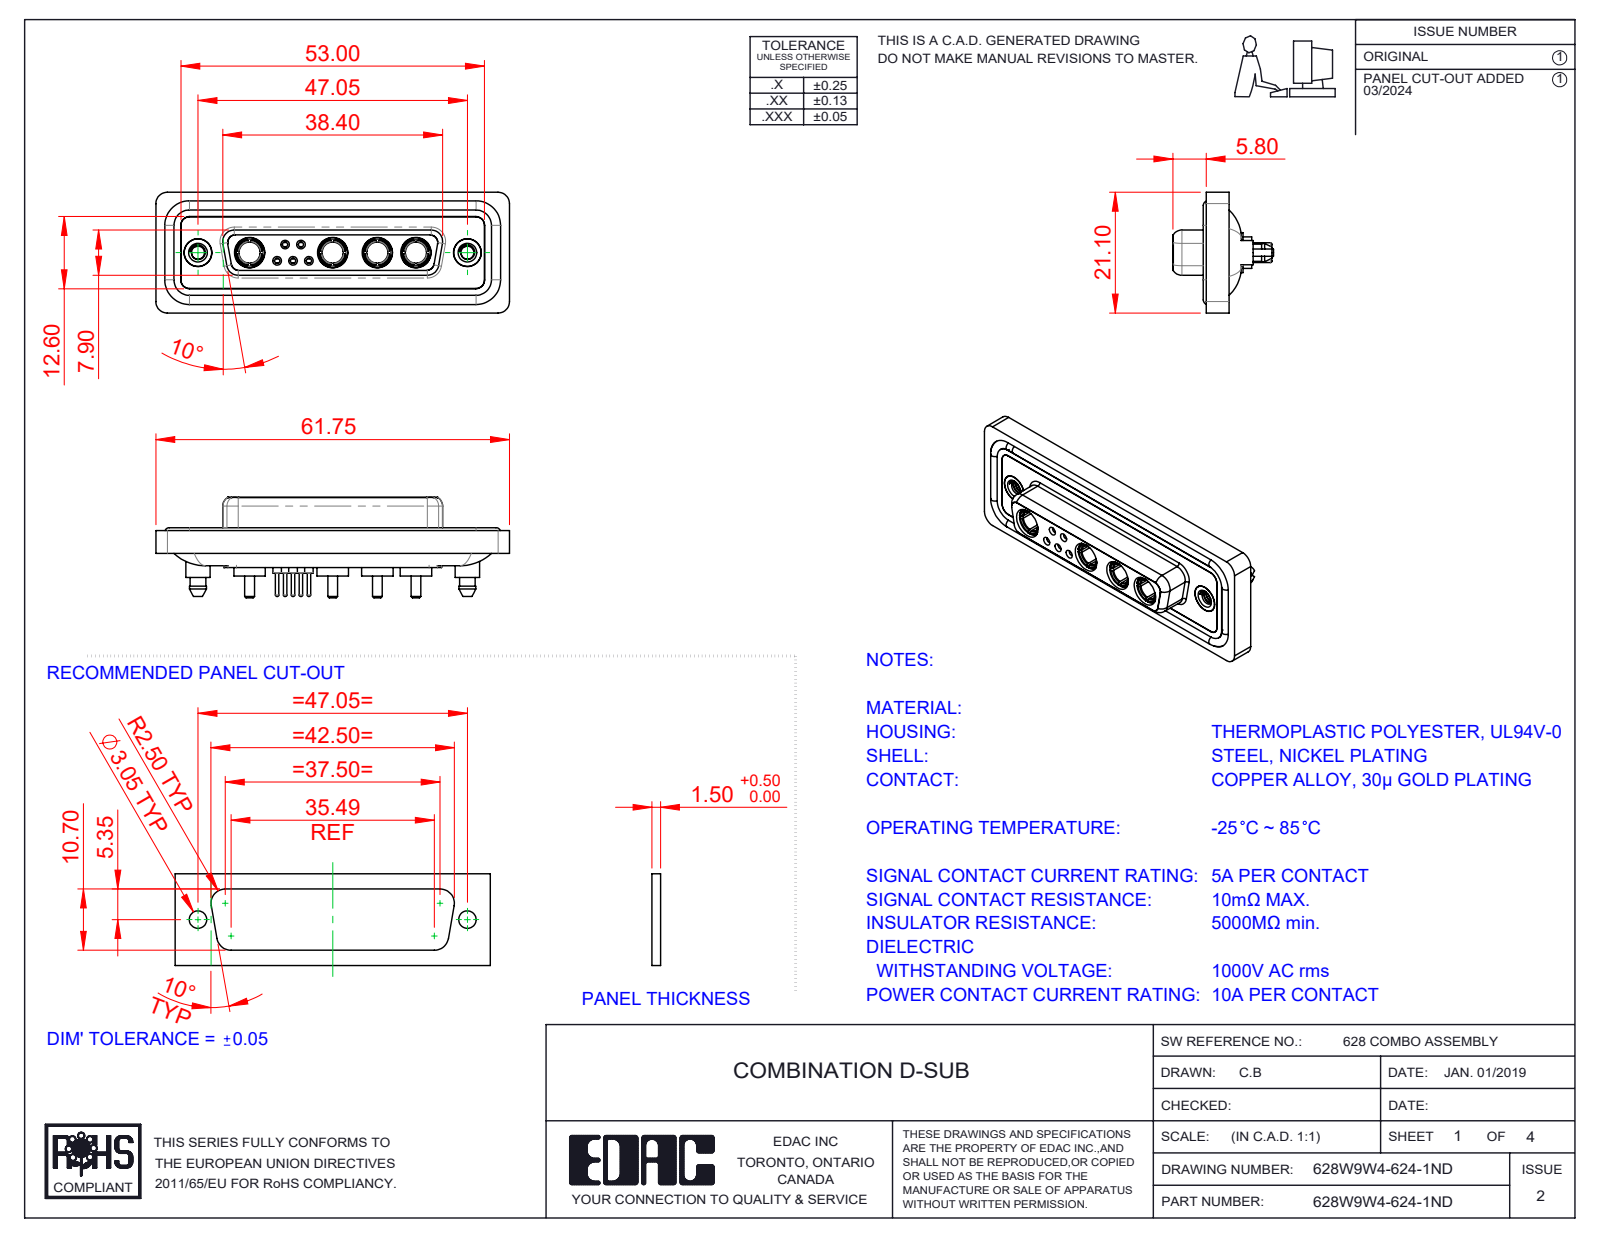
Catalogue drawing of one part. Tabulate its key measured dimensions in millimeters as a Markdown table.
| quantity | value |
| --- | --- |
| part name | 628Combo Waterproof Housing_25 Contacts; 628Combo Shell Rear_25 Contacts; 628Combo Contact Row 1_24; 628Combo Contact Row 2_24 (+5 more) |
| STEP written by | SolidWorks 2023 (CONFIG_CONTROL_DESIGN) |
| units | millimeters |
| bodies | 20 solids, 1023 faces (312 planar, 423 cylindrical, 288 other) |
| overall size | 61.75 × 21.1 × 17.55 |
| volume | 8 300 mm³ |
| surface area | 13 851 mm² |
| round holes (diameter × count) | 4.85 × 6, 0.9 × 5, 1.1 × 5, 1.5 × 5, 2 × 5, 3.7 × 4, 5.3 × 4, 1.6 × 3, 1.7 × 2, 2.26 × 2, 4 × 2, 4.05 × 2 |
| round bosses / shafts (diameter × count) | 1.6 × 6, 2.2 × 5, 0.6 × 5, 5.5 × 4, 5.2 × 4, 4.96 × 4, 4.75 × 4, 3.75 × 4 |
| partial cylindrical surfaces (radius × count) | 1.5 × 24, 2 × 18, 1.6 × 10, 1.35 × 8, 0.25 × 4, 0.5 × 4, 0.6 × 4, 0.65 × 4 |
| main face-to-face distances | 0.4, 1.8, 7.45, 5.65, 0.5, 7.05, 6.6, 1.6, 1.1, 2.9 |
| hole center spacings | 3.16, 2.77, 5.03, 2.76, 4.4, 5.02, 5.54, 5.73 |
